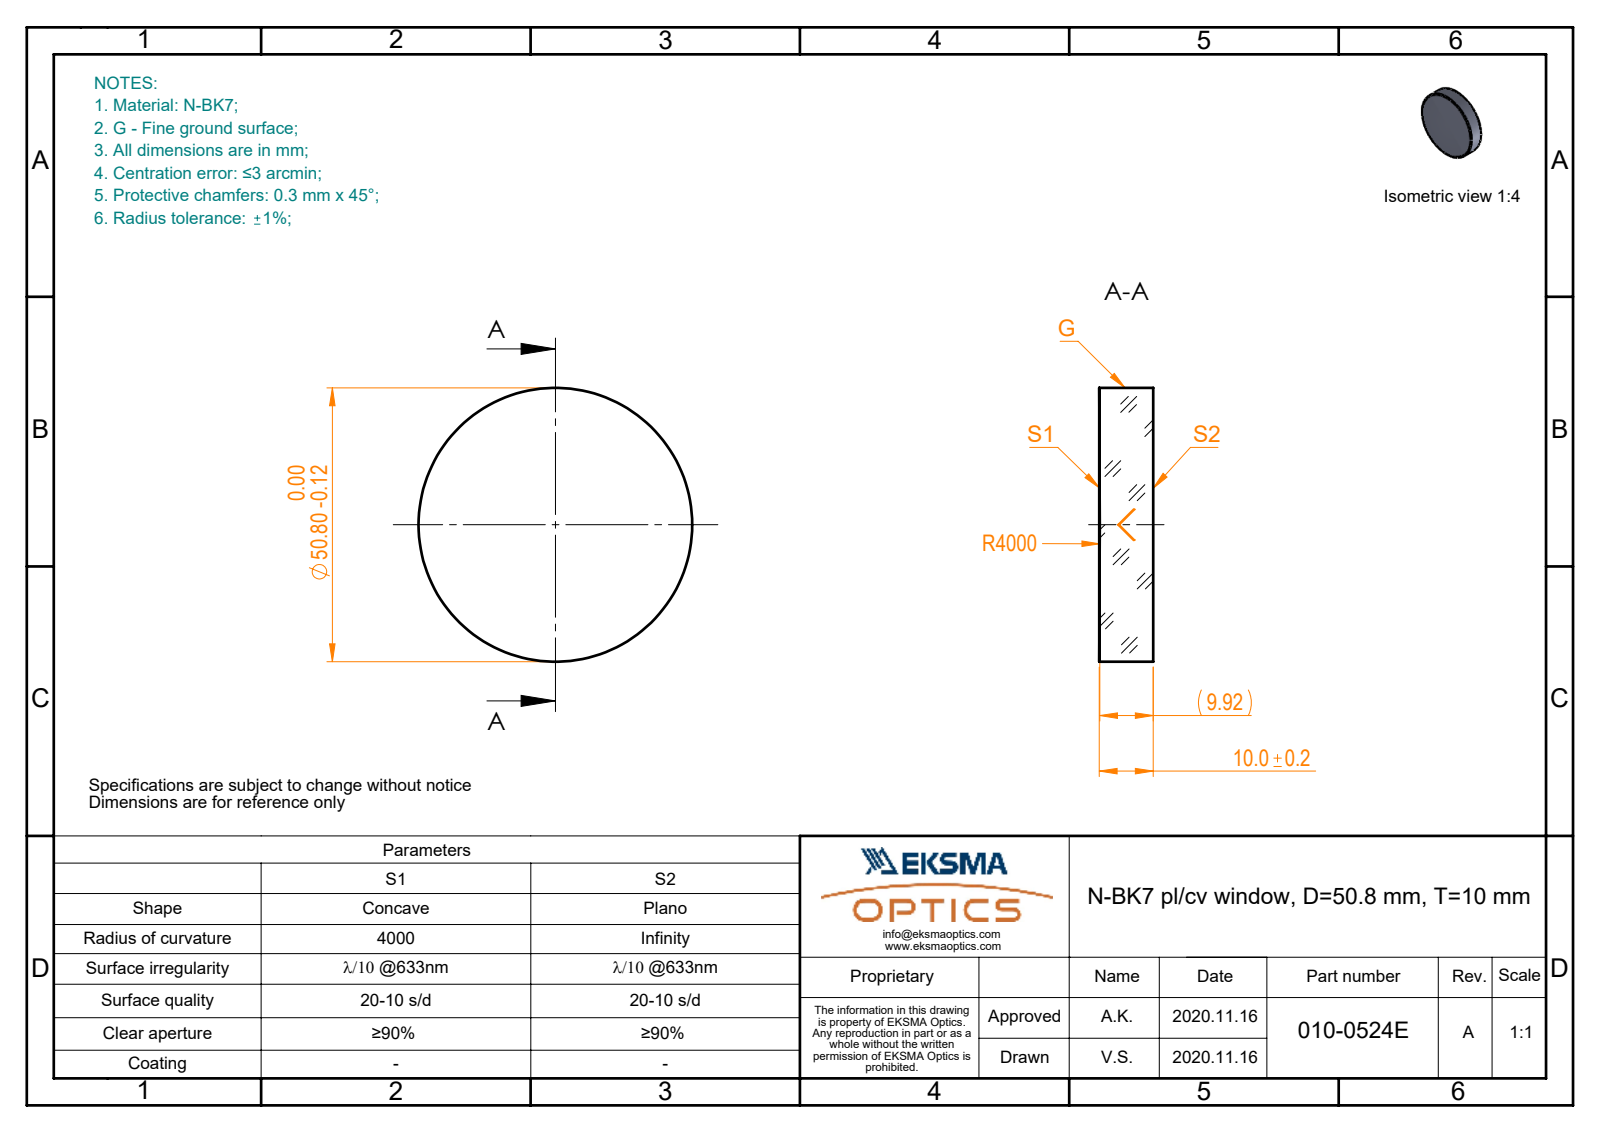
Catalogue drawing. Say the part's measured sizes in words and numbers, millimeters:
The part is named "010-0524E_N-BK7_PCV_window". Its 3-D file was written by "SolidWorks 2019 (CONFIG_CONTROL_DESIGN)". It is 1 solid with 5 faces: 1 planar, 2 cylindrical and 2 other. Overall it measures 50.8 by 50.8 by 10 millimeters. Its volume is 20 187 cubic millimeters and its surface area 5 650 square millimeters. Round bosses or shafts: 1 of diameter 50.8.
